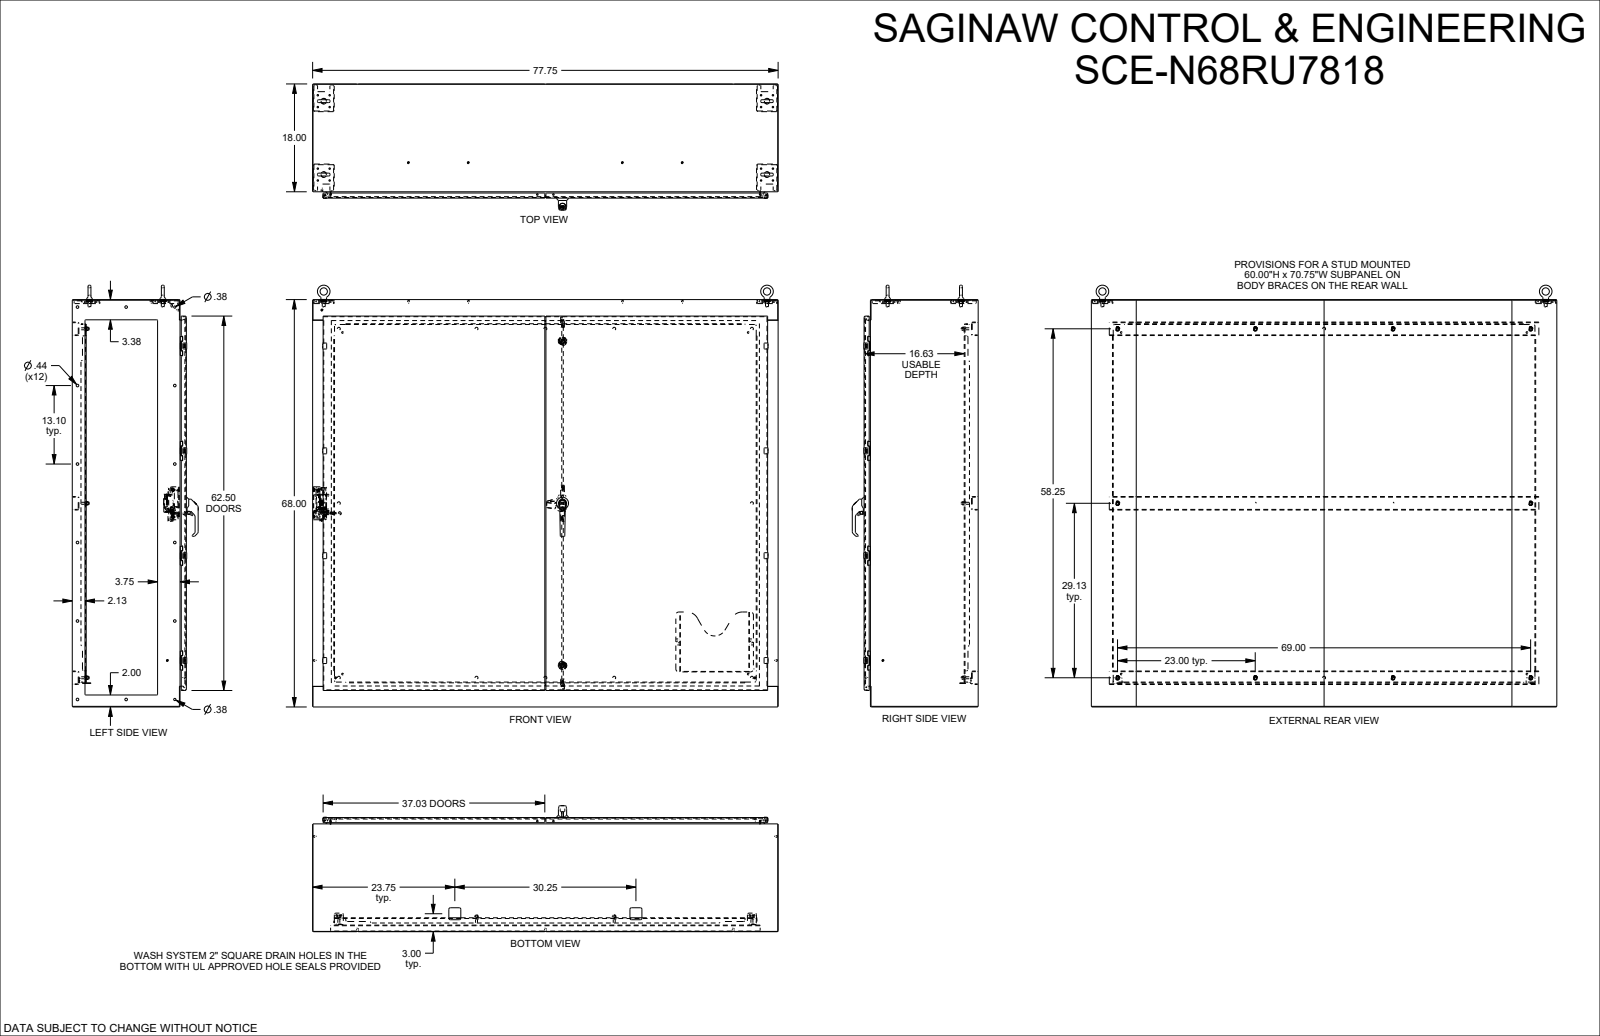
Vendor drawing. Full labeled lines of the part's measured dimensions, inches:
Part name (STEP PRODUCT): SCE-N68RU7818
STEP written by: SolidWorks 2023 (AUTOMOTIVE_DESIGN)
Units: inches
Bodies: 34 solids, 5036 faces (2373 planar, 1663 cylindrical, 1000 other)
Overall size (bounding box): 77.75 × 70.945 × 21.046
Volume: 1 805 in³ · Surface area: 34 613 in²
Round holes (diameter × count): ⌀0.25 ×19, ⌀0.375 ×18, ⌀0.244 ×16, ⌀0.437 ×12, ⌀0.04 ×8, ⌀0.205 ×8, ⌀0.205 ×8, ⌀0.218 ×8, ⌀0.17 ×4, ⌀0.256 ×4, ⌀0.875 ×4, ⌀0.206 ×2
Round bosses / shafts (diameter × count): ⌀0.17 ×24, ⌀0.25 ×16, ⌀0.24 ×16, ⌀0.196 ×10, ⌀1.173 ×4, ⌀0.6 ×4, ⌀1.4 ×2, ⌀0.406 ×2
Partial cylindrical surfaces — rounded edges, fillets, slot ends (radius × count): R0.03 ×102, R0.015 ×90, R0.125 ×67, R0.062 ×66, R0.04 ×41, R0.167 ×38, R0.229 ×32, R0.1 ×25
Main face-to-face distances: 0.104, 18.954, 18.85, 19.058, 67.896, 17.896, 1.058, 68, 67.792, 1
Hole centre spacings: 17.5, 1.979, 35, 72.868, 1.4, 13.1, 20.873, 74.9
